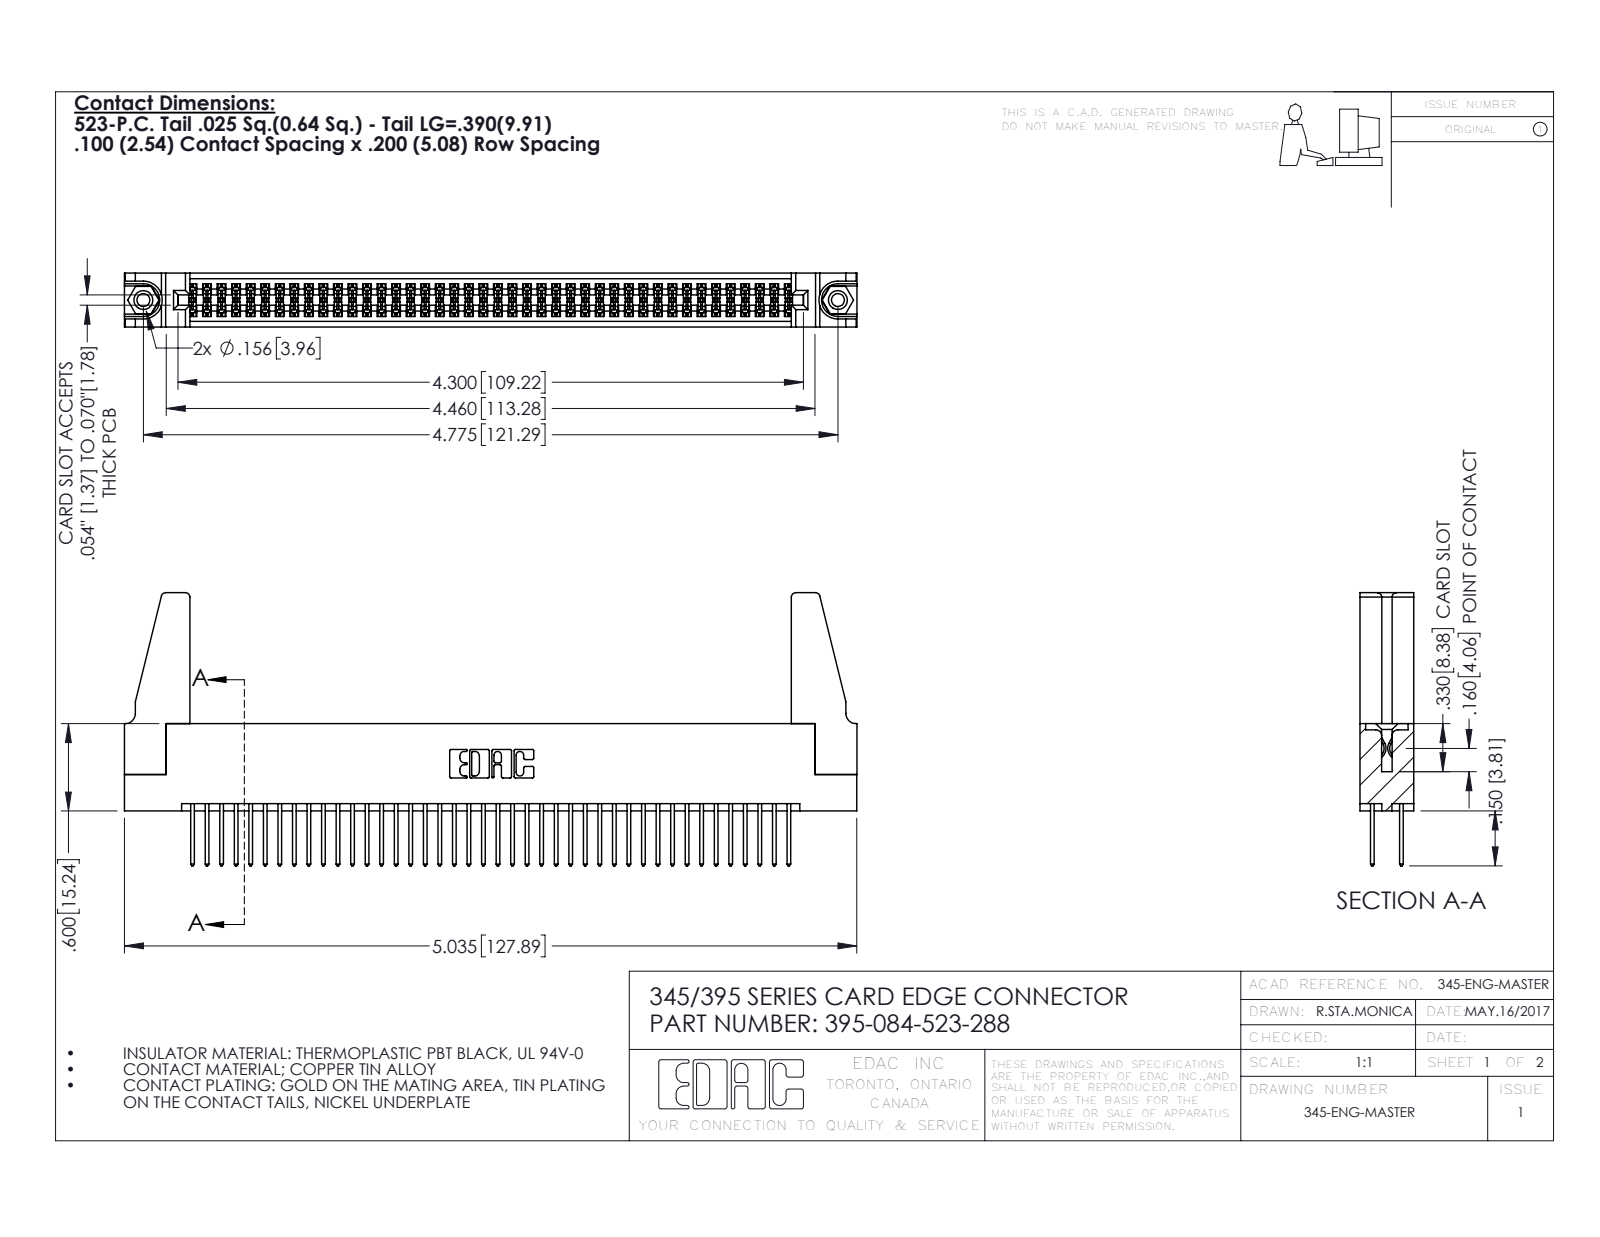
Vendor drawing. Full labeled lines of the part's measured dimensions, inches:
Part name (STEP PRODUCT): 345-292-001_345-293-123; 395-084-523-288; 345-220-078_345-220-088; 345-250-001_345-250-001-102 (+1 more)
STEP written by: SolidWorks 2016 (CONFIG_CONTROL_DESIGN)
Units: inches
Bodies: 89 solids, 4450 faces (2924 planar, 1510 cylindrical, 16 other)
Overall size (bounding box): 5.036 × 1.877 × 0.37
Volume: 0.967 in³ · Surface area: 34.9 in²
Round holes (diameter × count): ⌀0.089 ×2, ⌀0.125 ×2, ⌀0.156 ×2, ⌀0.064 ×1
Round bosses / shafts (diameter × count): ⌀0.155 ×2
Partial cylindrical surfaces — rounded edges, fillets, slot ends (radius × count): R0.006 ×126, R0.01 ×84, R0.01 ×22, R0.03 ×8, R0.007 ×6, R0.031 ×6, R0.026 ×3, R0.014 ×2
Main face-to-face distances: 0.072, 0.298, 0.2, 0.37, 0.098, 0.272, 0.025, 0.225, 0.175, 0.149
Hole centre spacings: 0.27, 4.539, 4.775
